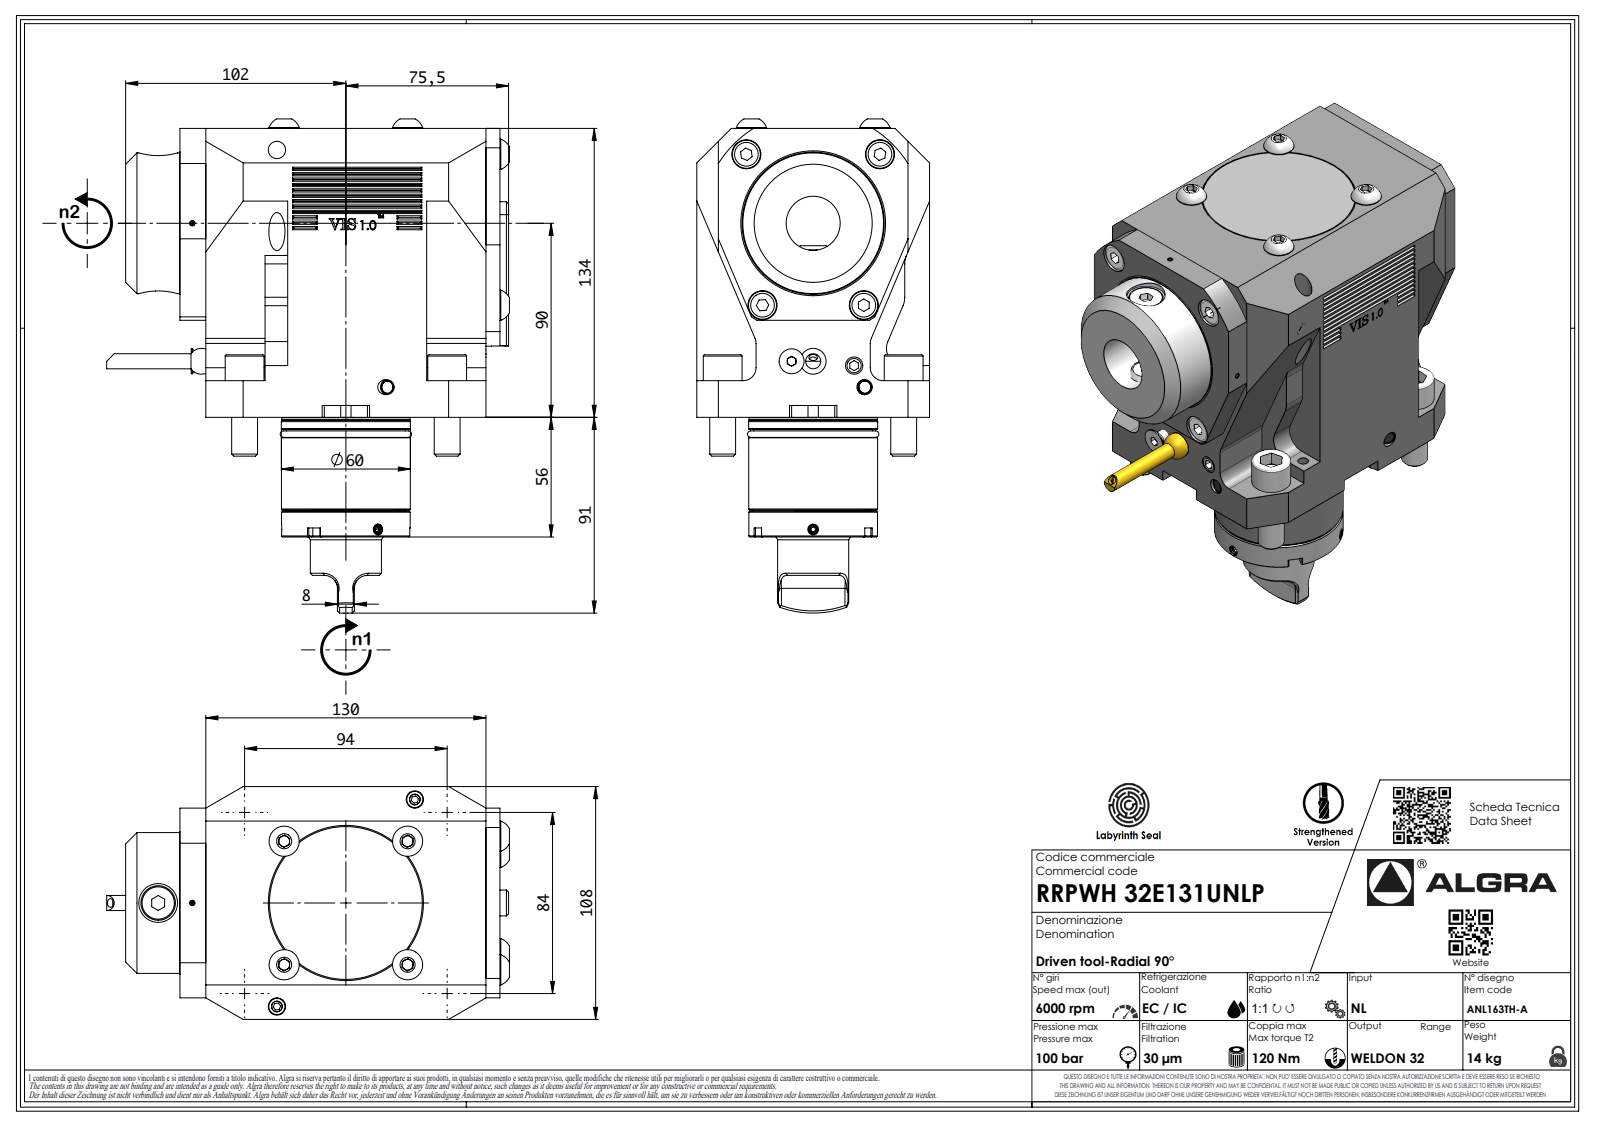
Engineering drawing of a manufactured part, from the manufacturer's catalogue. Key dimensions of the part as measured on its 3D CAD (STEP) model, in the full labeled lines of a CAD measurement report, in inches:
Part name (STEP PRODUCT): RRPWH32E131UNLP
STEP written by: SolidWorks 2023 (AUTOMOTIVE_DESIGN)
Units: inches
Bodies: 1 solid, 947 faces (642 planar, 118 cylindrical, 187 other)
Overall size (bounding box): 8.85 × 7.343 × 4.252
Volume: 124.6 in³ · Surface area: 201.4 in²
Round holes (diameter × count): ⌀0.083 ×1, ⌀0.157 ×1, ⌀0.551 ×1, ⌀0.709 ×1, ⌀0.988 ×1
Round bosses / shafts (diameter × count): ⌀0.709 ×4, ⌀0.472 ×4, ⌀2.571 ×1, ⌀2.358 ×1, ⌀2.354 ×1, ⌀2.35 ×1, ⌀2.343 ×1, ⌀2.173 ×1
Partial cylindrical surfaces — rounded edges, fillets, slot ends (radius × count): R0.008 ×21, R0.315 ×18, R0.236 ×11, R0.013 ×7, R0.02 ×7, R0.146 ×7, R0.394 ×4, R0.118 ×3
Main face-to-face distances: 5.276, 4.252, 0.472, 1.083, 4.035, 5.846, 0.256, 5.374, 1.496, 0.217
